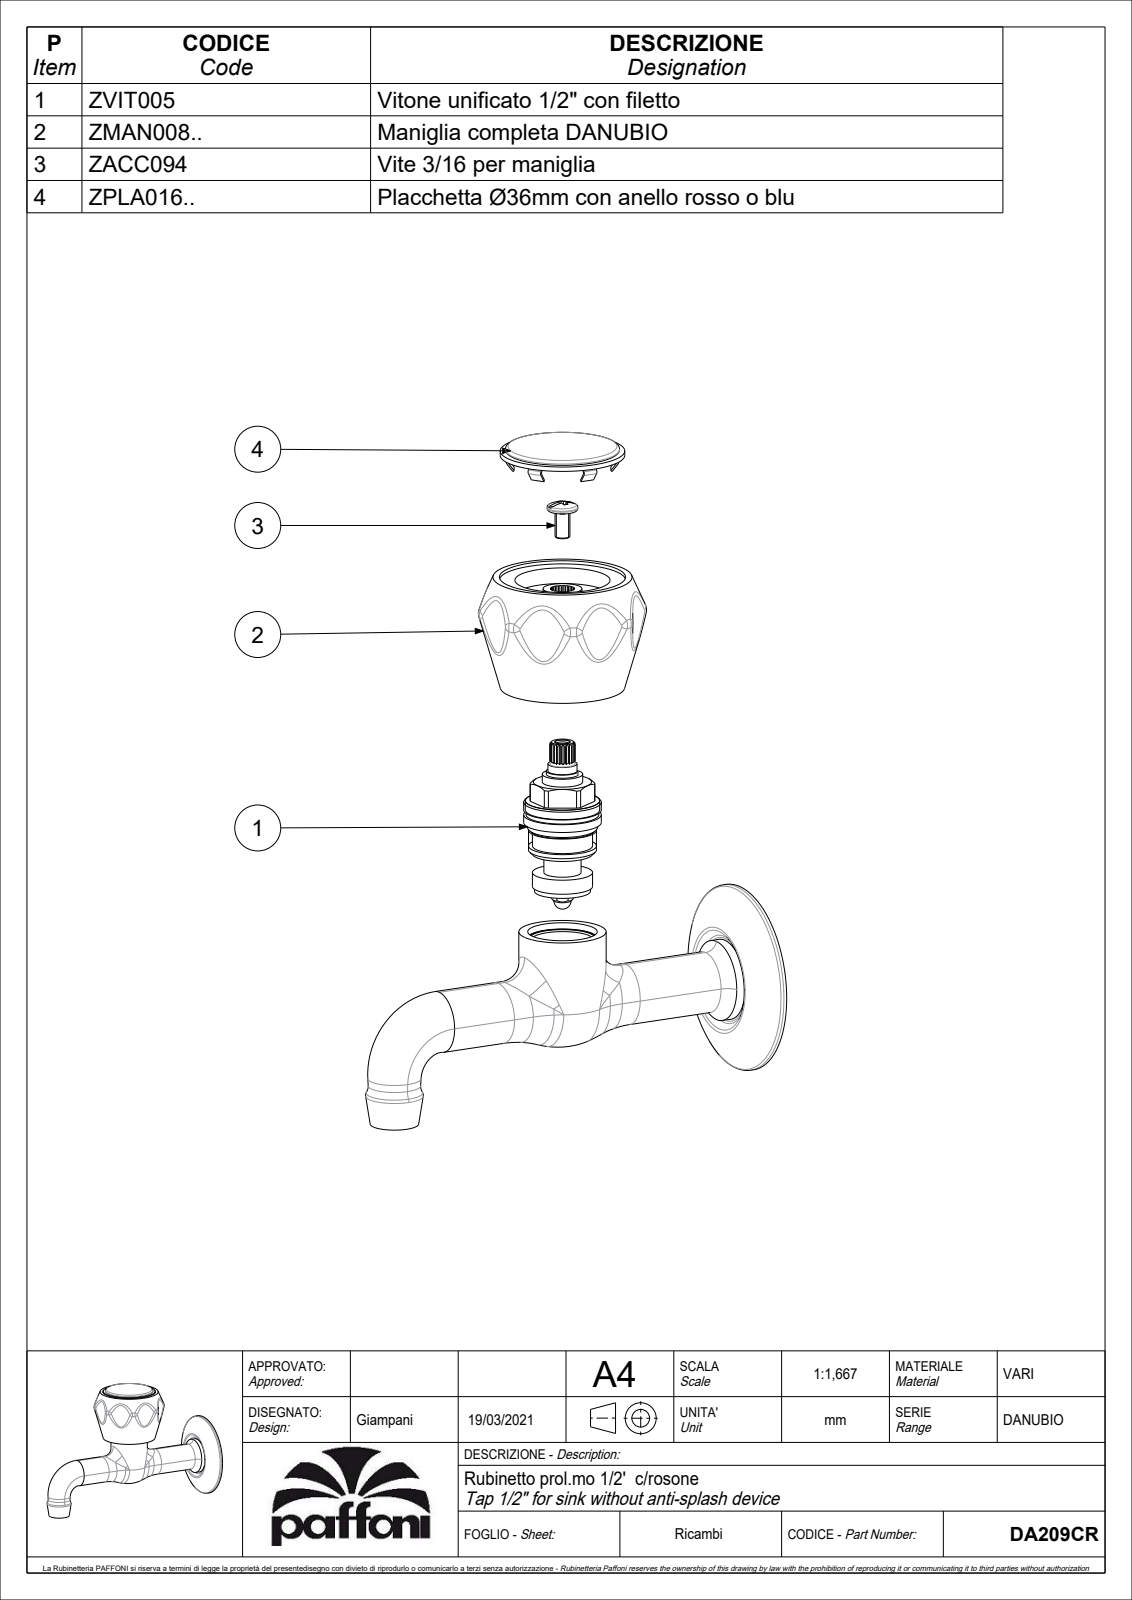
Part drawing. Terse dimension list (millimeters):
name: DA209CR
written by: CREO PARAMETRIC BY PTC INC, 2020044 (CONFIG_CONTROL_DESIGN)
unit: mm
bodies: 1 solid, 145 faces (7 planar, 18 cylindrical, 120 other)
size: 139.92 × 90.5 × 58
volume: 126 945 mm³; area: 23 098 mm²
bosses: 1× ⌀58, 1× ⌀38.5, 1× ⌀27, 1× ⌀25, 1× ⌀21
rounds: 8× R21.31
face distances: 7.7, 35.3, 35.7, 0.4, 51.8, 87.1, 87.5, 13, 5.3
